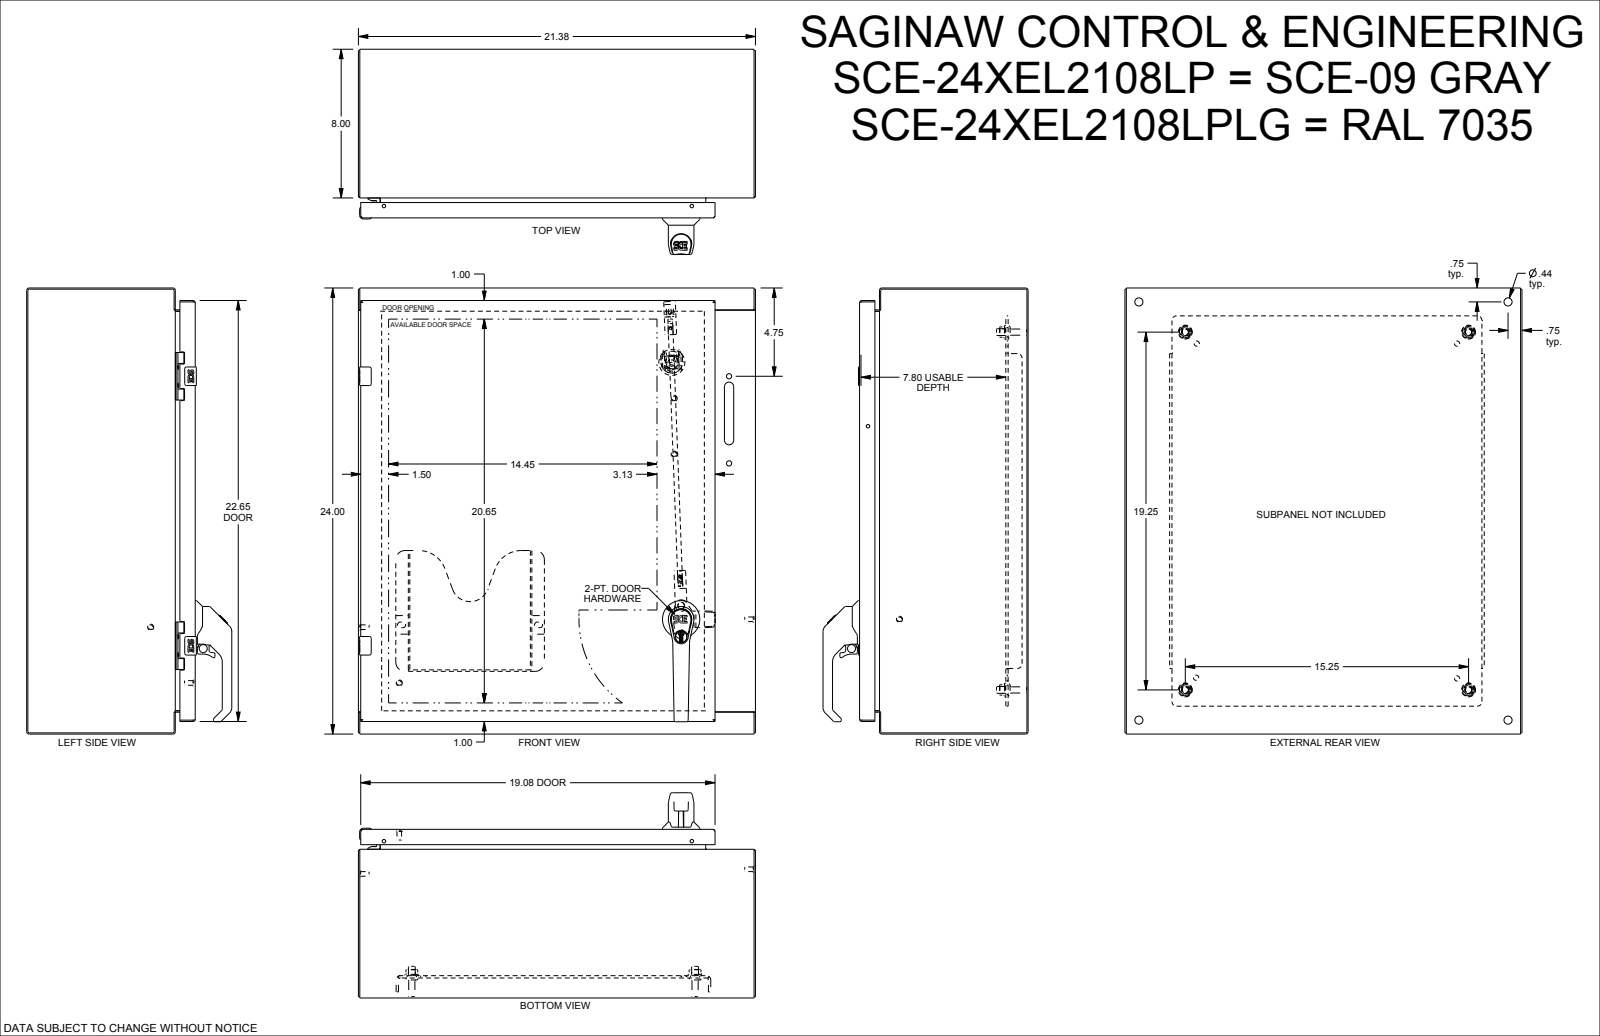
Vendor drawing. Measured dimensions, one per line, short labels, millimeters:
name: SCE-24XEL2108LPLG
written by: SolidWorks 2019 (CONFIG_CONTROL_DESIGN)
unit: mm
bodies: 0 solids, 4608 faces (1739 planar, 1214 cylindrical, 1655 other)
size: 609.6 × 542.9 × 280.4
holes: 6× ⌀7.1, 5× ⌀6.8, 4× ⌀4.4, 4× ⌀5.2, 4× ⌀6.2, 4× ⌀9.3, 4× ⌀9.5, 4× ⌀11.1, 4× ⌀12.7, 3× ⌀6.4, 2× ⌀1, 2× ⌀3.5
bosses: 8× ⌀6.3, 6× ⌀4.3, 5× ⌀6.4, 4× ⌀9.3, 4× ⌀8.4, 4× ⌀6.1, 3× ⌀14.3, 3× ⌀5
rounds: 71× R0.8, 54× R0.4, 43× R0.5, 36× R0.5, 32× R0.3, 30× R1, 26× R0.1, 25× R1
face distances: 1.9, 1.9, 228.5, 226.6, 230.5, 228.5, 541, 3.2, 201.2, 30.5
hole spacings: 368.3, 25, 0.5, 12.5, 12.5, 114.1, 12, 18.4
